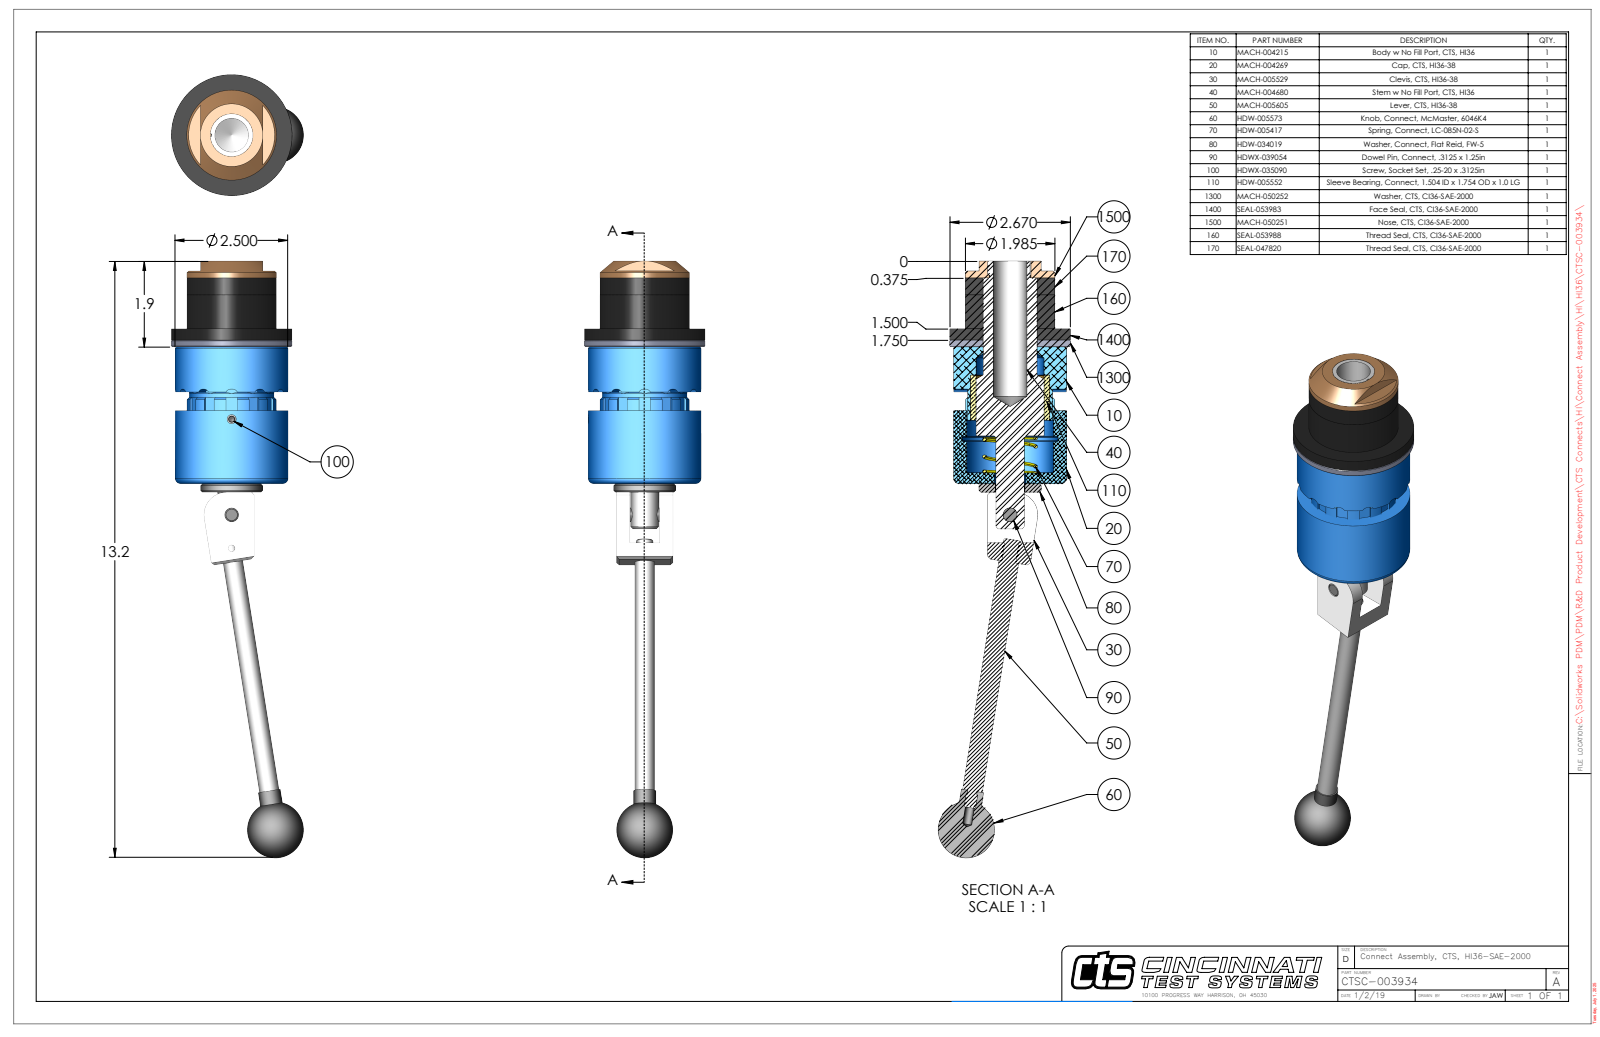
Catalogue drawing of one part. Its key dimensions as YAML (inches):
part_name: "CTSC-003934"
step_written_by: "SolidWorks 2023 (AUTOMOTIVE_DESIGN)"
units: inches
bodies: {solids: 11, faces: 373, planar: 162, cylindrical: 132, other: 79}
overall_size: [13.215, 2.93, 2.675]
volume: 22.82
surface_area: 133.5
round_holes:
  - {diameter: 0.201, count: 2}
  - {diameter: 0.15, count: 1}
  - {diameter: 0.311, count: 1}
  - {diameter: 0.313, count: 1}
  - {diameter: 0.314, count: 1}
  - {diameter: 0.656, count: 1}
  - {diameter: 0.696, count: 1}
  - {diameter: 0.75, count: 1}
  - {diameter: 0.922, count: 1}
  - {diameter: 1.19, count: 1}
  - {diameter: 1.196, count: 1}
round_bosses_or_shafts:
  - {diameter: 2.675, count: 1}
  - {diameter: 2.67, count: 1}
  - {diameter: 2.5, count: 1}
  - {diameter: 1.985, count: 1}
  - {diameter: 1.98, count: 1}
  - {diameter: 1.875, count: 1}
  - {diameter: 1.38, count: 1}
  - {diameter: 1.186, count: 1}
partial_cylinders:
  - {radius: 0.12, count: 12}
  - {radius: 0.029, count: 2}
  - {radius: 0.5, count: 1}
  - {radius: 0.961, count: 1}
  - {radius: 0.996, count: 1}
  - {radius: 1.168, count: 1}
face_to_face_distances: [0.15, 0.25, 0.4, 1, 0.75, 1.15, 1.375, 1.125, 1.525, 3.03]
hole_center_spacings: [0.74, 2.118, 2.858]
